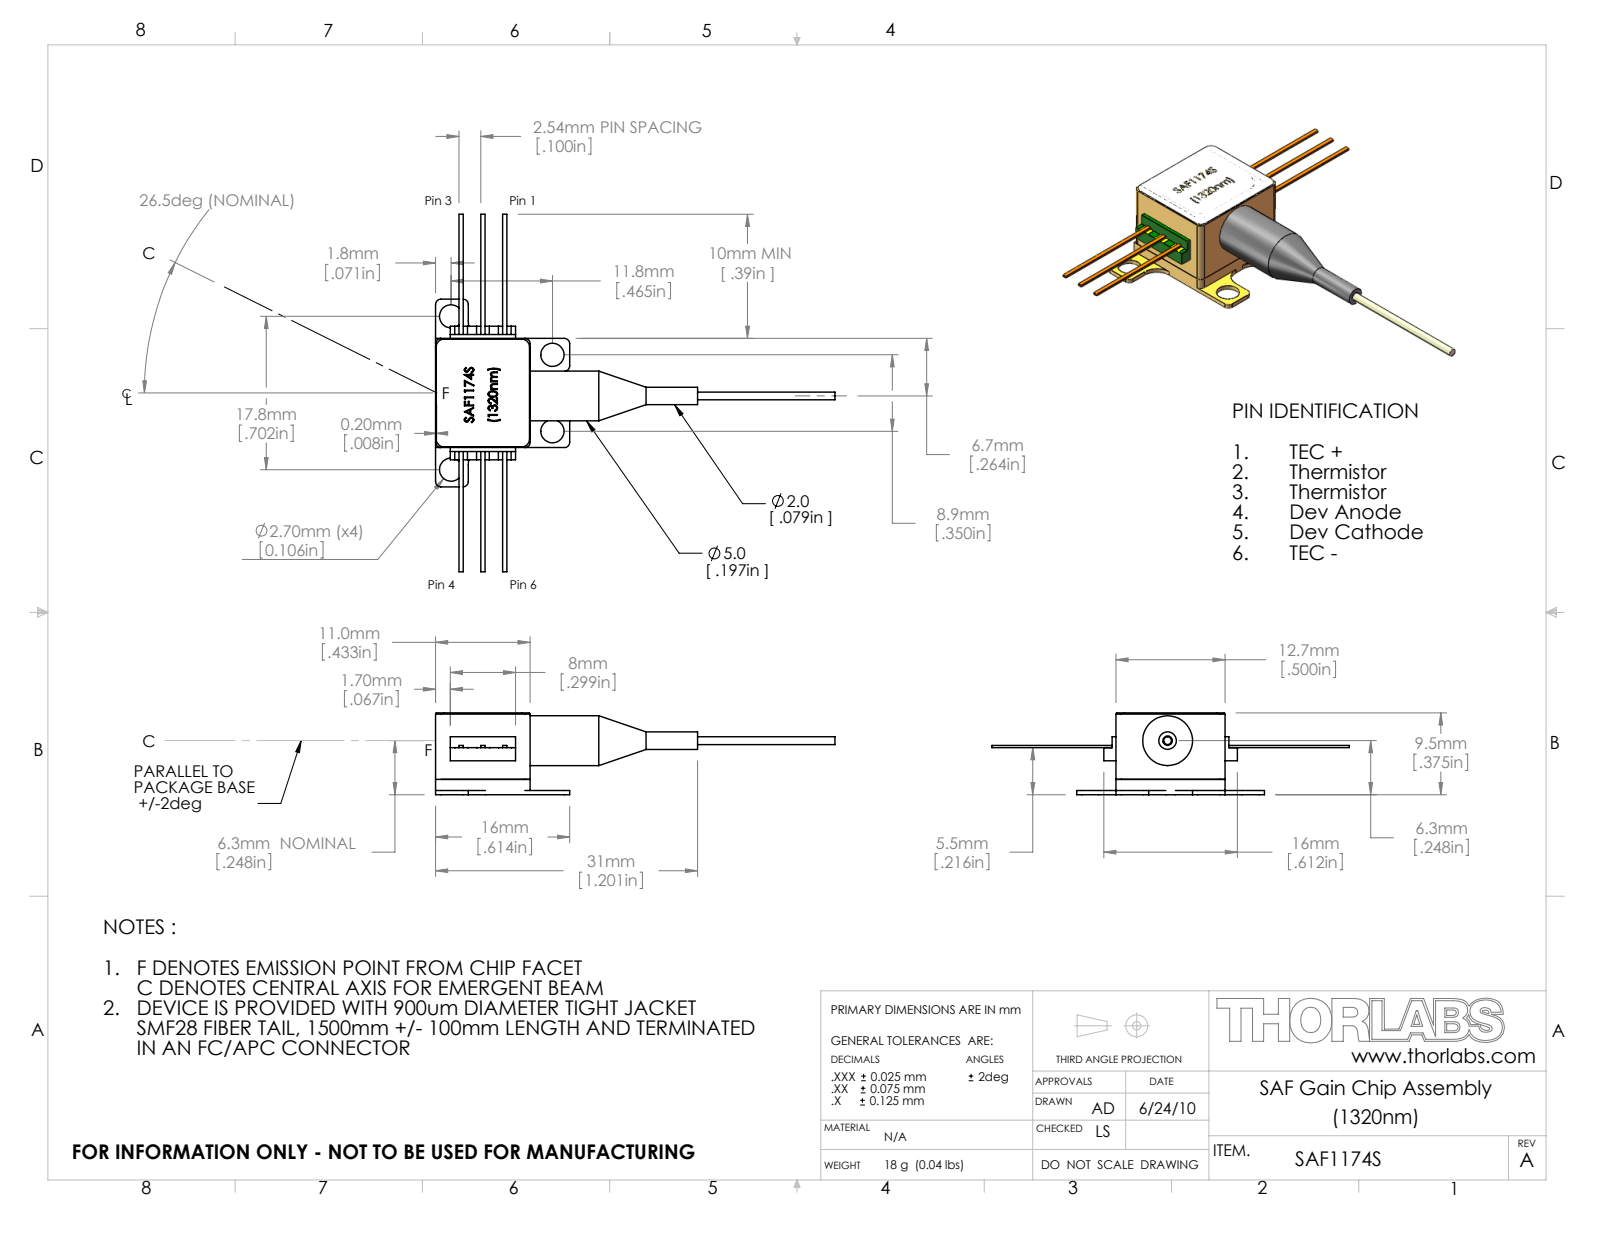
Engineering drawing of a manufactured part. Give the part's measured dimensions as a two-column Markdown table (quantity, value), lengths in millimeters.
| quantity | value |
| --- | --- |
| part name | 20745.E0W |
| STEP written by | SolidWorks 2009 (AUTOMOTIVE_DESIGN) |
| units | millimeters |
| bodies | 0 solids, 275 faces (191 planar, 44 cylindrical, 40 other) |
| overall size | 46.5 × 41.6 × 9.53 |
| round holes (diameter × count) | 2.7 × 4, 1.1 × 1 |
| round bosses / shafts (diameter × count) | 5.8 × 1, 2.04 × 1, 0.9 × 1 |
| partial cylindrical surfaces (radius × count) | 0.6 × 12, 0.9 × 4, 2 × 4, 0.3 × 2, 1 × 2, 1.85 × 2 |
| main face-to-face distances | 9.52, 9.4, 1, 11.7, 7.8, 1.6, 1.45, 9.14, 0.38, 7.6 |
| hole center spacings | 12.62, 17.83, 8.9, 17.84 |
